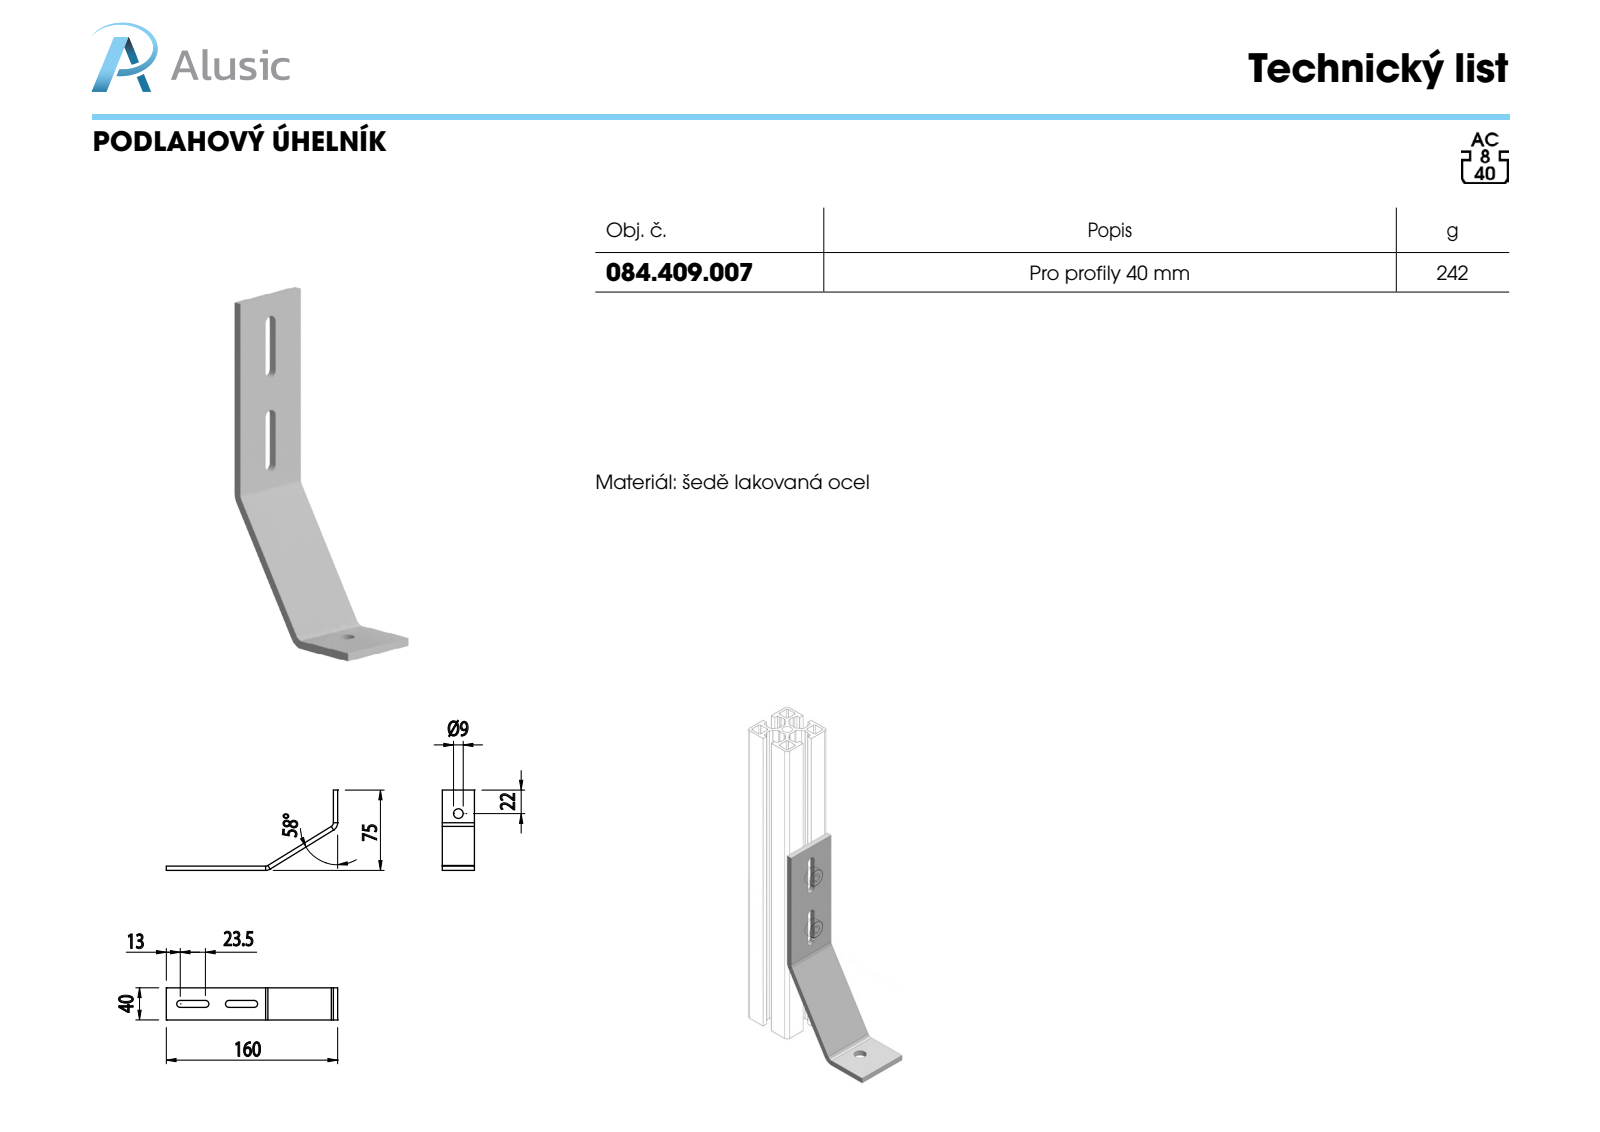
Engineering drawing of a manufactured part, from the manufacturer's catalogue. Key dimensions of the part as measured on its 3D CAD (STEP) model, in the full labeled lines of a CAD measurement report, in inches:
Part name (STEP PRODUCT): 084.409.007
STEP written by: SolidWorks 2011 (CONFIG_CONTROL_DESIGN)
Units: inches
Bodies: 1 solid, 32 faces (22 planar, 10 cylindrical, 0 other)
Overall size (bounding box): 6.299 × 2.953 × 1.575
Volume: 1.869 in³ · Surface area: 27.75 in²
Round holes (diameter × count): ⌀0.354 ×1
Partial cylindrical surfaces — rounded edges, fillets, slot ends (radius × count): R0.128 ×4, R0.157 ×2, R0.315 ×2
Main face-to-face distances: 0.157, 1.575, 0.659, 0.915, 0.256, 2.953, 2.795, 6.299, 6.142
